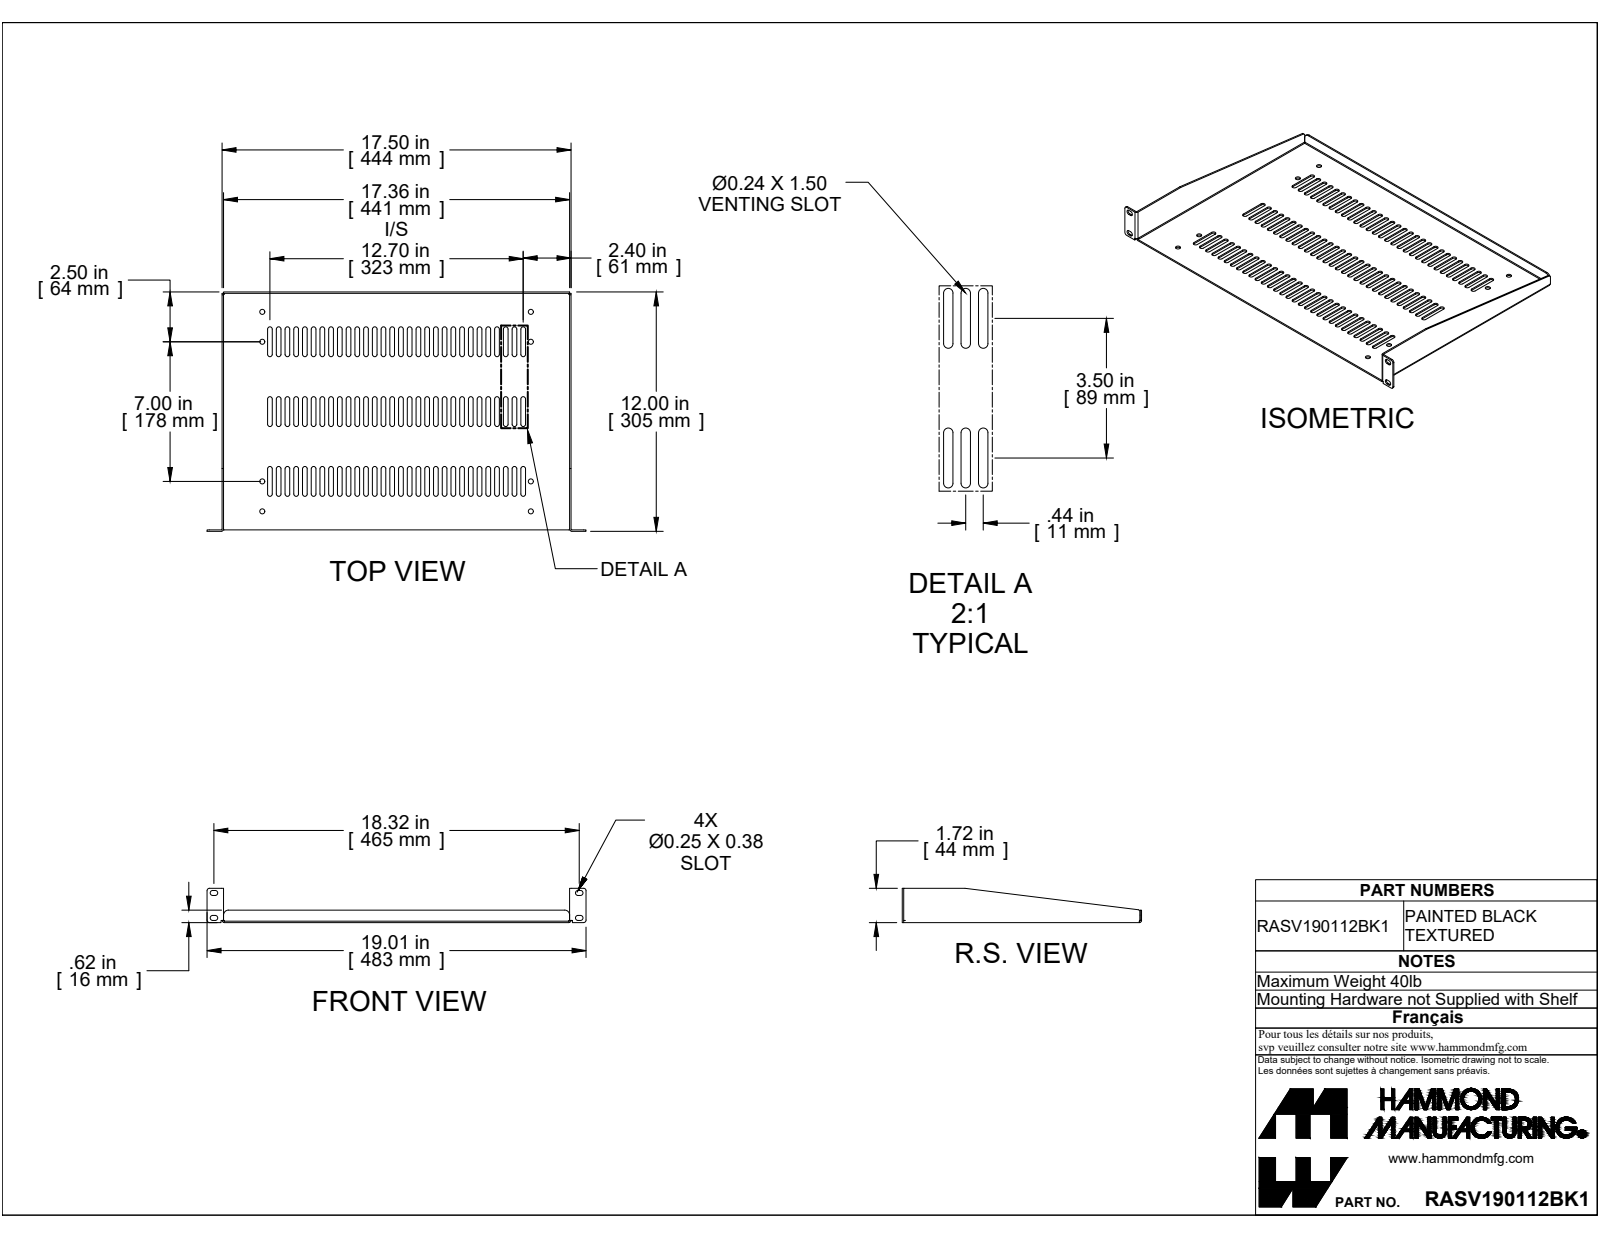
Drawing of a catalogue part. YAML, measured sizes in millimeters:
part_name: "RASV190112BK1"
step_written_by: "SolidWorks 2019 (CONFIG_CONTROL_DESIGN)"
units: millimeters
bodies: {solids: 1, faces: 448, planar: 228, cylindrical: 216, other: 4}
overall_size: [482.8, 304.8, 43.6]
volume: 256900
surface_area: 298400
round_holes:
  - {diameter: 6.4, count: 8}
partial_cylinders:
  - {radius: 3, count: 174}
  - {radius: 3.2, count: 12}
  - {radius: 3, count: 6}
  - {radius: 0.9, count: 5}
  - {radius: 2.7, count: 5}
  - {radius: 1.4, count: 3}
  - {radius: 6.4, count: 2}
face_to_face_distances: [1.8, 442.7, 440.8, 444.5, 22.3, 301.1, 303, 44.5, 66.8, 11.1]
hole_center_spacings: [38.1, 215.9, 342.1, 344.2, 404.5, 177.8, 254, 385.5]
